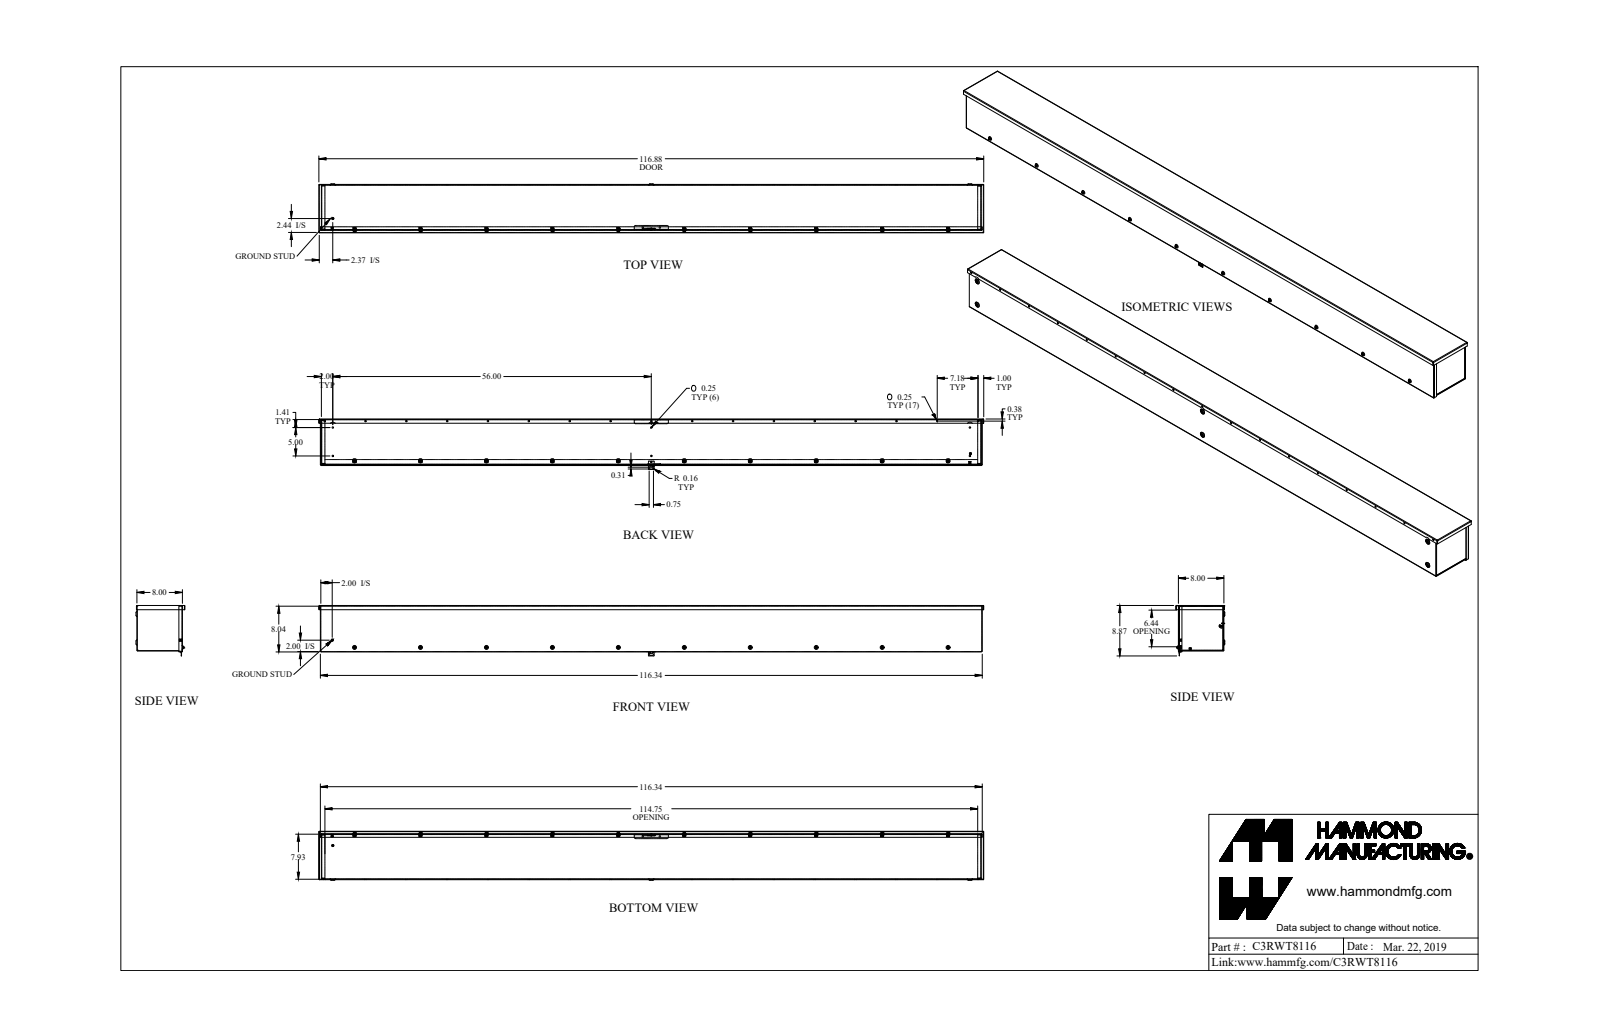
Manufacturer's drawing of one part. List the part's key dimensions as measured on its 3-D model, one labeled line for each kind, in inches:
Part name (STEP PRODUCT): C3RWT8116_Default
STEP written by: SolidWorks 2019 (CONFIG_CONTROL_DESIGN)
Units: inches
Bodies: 44 solids, 1696 faces (925 planar, 547 cylindrical, 224 other)
Overall size (bounding box): 116.875 × 8.871 × 8.594
Volume: 306.1 in³ · Surface area: 8 586 in²
Round holes (diameter × count): ⌀0.25 ×25, ⌀0.156 ×12, ⌀0.214 ×10, ⌀0.23 ×10, ⌀0.203 ×2, ⌀0.125 ×1, ⌀0.137 ×1, ⌀0.2 ×1, ⌀0.215 ×1
Round bosses / shafts (diameter × count): ⌀0.19 ×11, ⌀0.148 ×10, ⌀0.375 ×2, ⌀0.5 ×1, ⌀0.367 ×1, ⌀0.21 ×1, ⌀0.152 ×1, ⌀0.125 ×1
Partial cylindrical surfaces — rounded edges, fillets, slot ends (radius × count): R0.08 ×40, R0.108 ×40, R0.022 ×20, R0.036 ×18, R0.108 ×18, R0.125 ×18, R0.171 ×10, R0.206 ×10
Main face-to-face distances: 0.072, 7.928, 8, 0.072, 7.856, 7.856, 7.928, 0.144, 8.366, 0.51
Hole centre spacings: 11.594, 7.18, 14.359, 21.539, 35.898, 23.187, 23.188, 34.781
